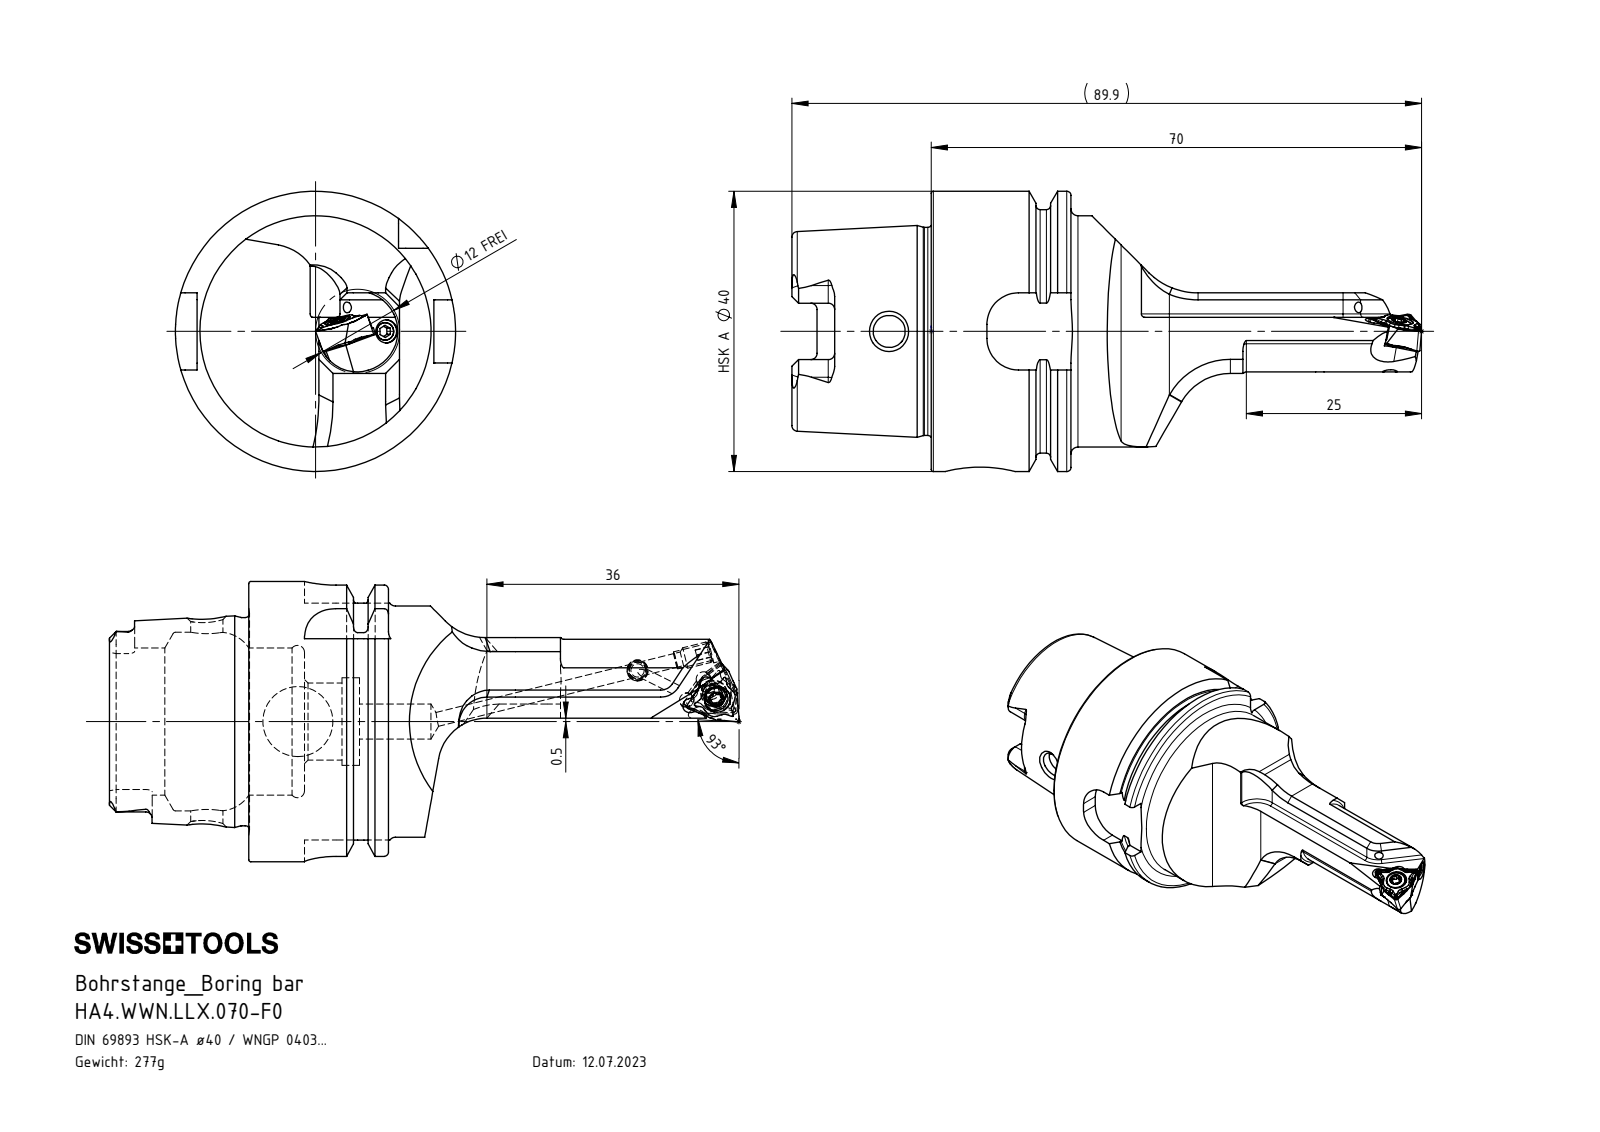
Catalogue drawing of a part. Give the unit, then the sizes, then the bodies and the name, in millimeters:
Units: millimetres
Overall size (bounding box): 89.92 × 40 × 40
Round holes (diameter × count): ⌀2.1 ×2, ⌀2.5 ×2, ⌀1.5 ×1, ⌀2 ×1, ⌀2.05 ×1, ⌀2.7 ×1, ⌀3.3 ×1, ⌀3.5 ×1, ⌀4.6 ×1, ⌀5 ×1, ⌀10 ×1, ⌀11 ×1
Round bosses / shafts (diameter × count): ⌀3 ×2, ⌀40 ×1, ⌀34.75 ×1, ⌀33 ×1, ⌀29.71 ×1, ⌀3.4 ×1, ⌀2.5 ×1
Partial cylindrical surfaces — rounded edges, fillets, slot ends (radius × count): R0.35 ×48, R0.2 ×24, R1 ×18, R0.25 ×12, R0.21 ×6, R0.44 ×6, R0.9 ×6, R1.8 ×6
Main face-to-face distances: 7.95, 19.95, 12, 19.9, 27.85, 39.85, 17.4, 11.5, 35.7, 15.8
Hole centre spacings: 2.56, 2.64, 3.85, 3.87, 4, 49.05
Volume: 35 341 mm³ · Surface area: 12 580 mm²
Bodies: 5 solids, 816 faces (194 planar, 245 cylindrical, 377 other)
Part name (STEP PRODUCT): HA4.WWN.LLX.070-F0; ISO 4026 - M3 x 4_PreviewCfg; WCA-ER2.001.006_B; WXGU040304R-TS (+1 more)
STEP written by: SolidWorks 2022 (AUTOMOTIVE_DESIGN)
